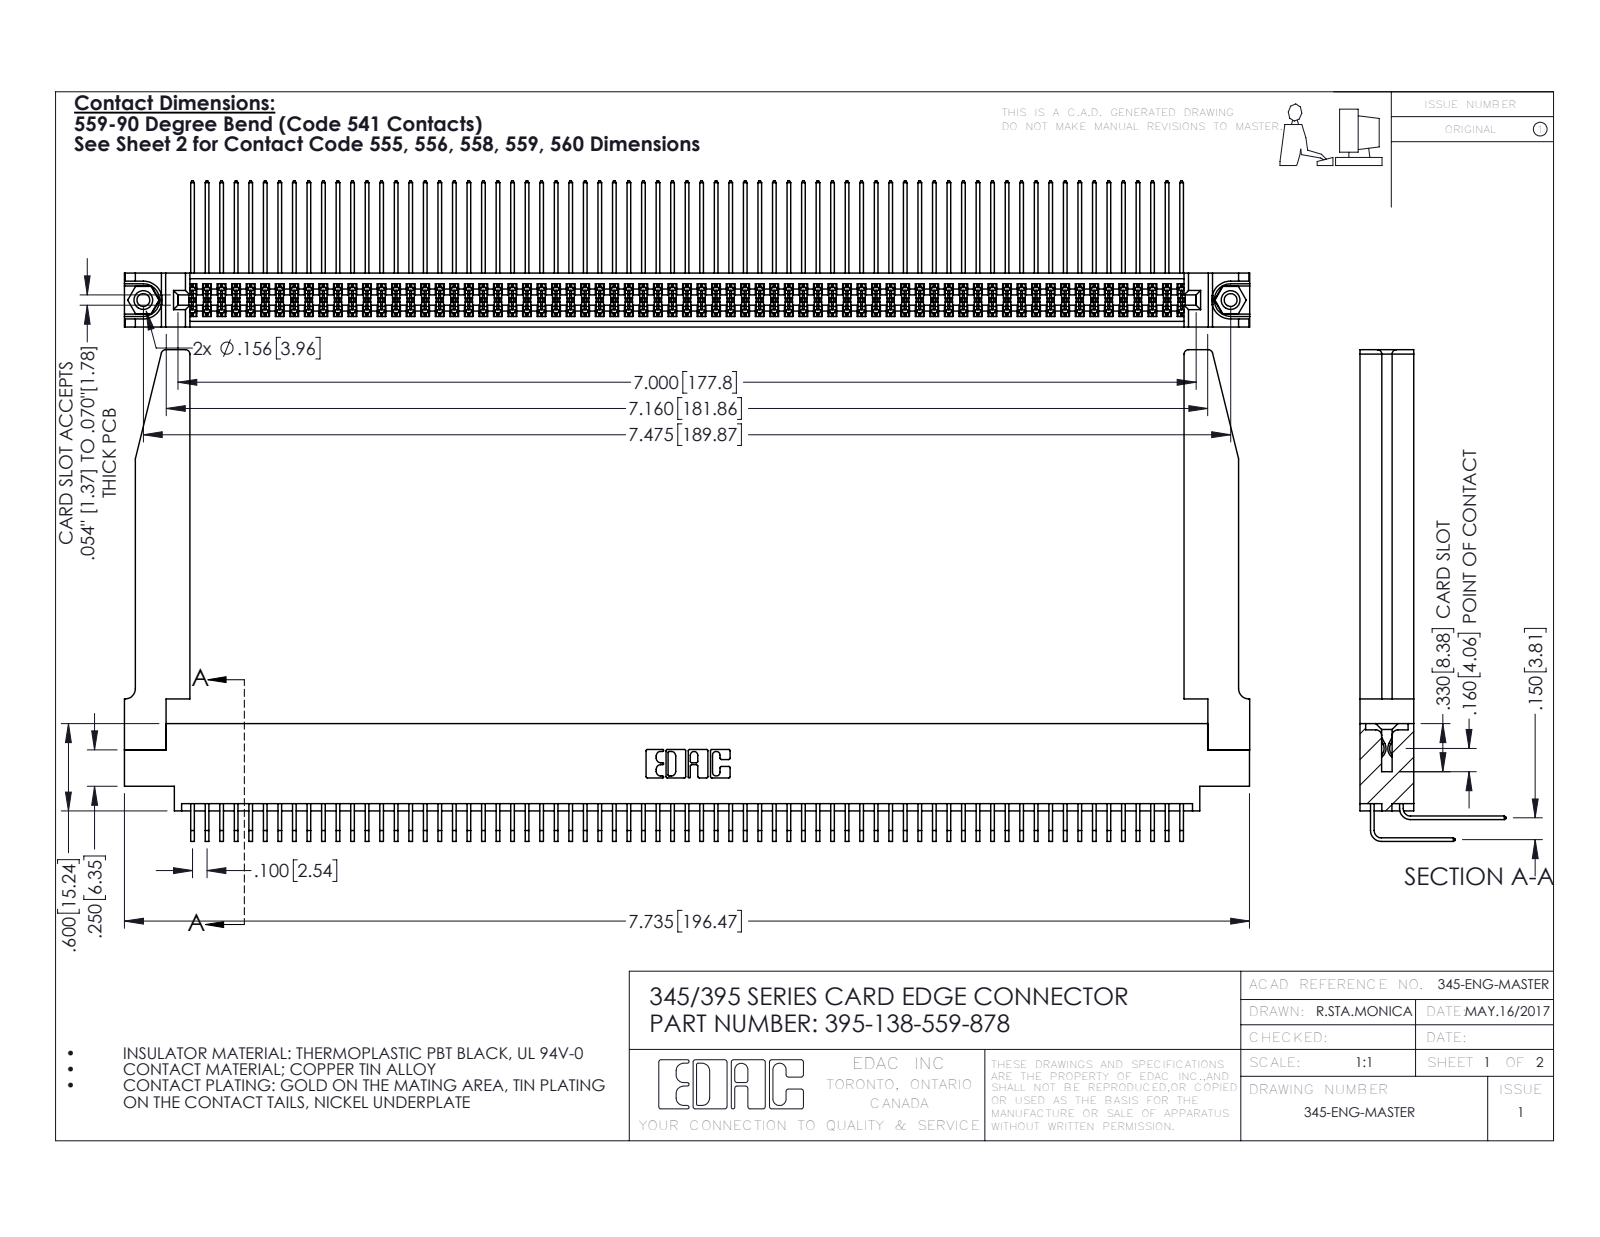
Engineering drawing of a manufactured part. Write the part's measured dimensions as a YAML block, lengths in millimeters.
part_name: "395-138-559-878; 345-292-001_559 Tail - 2; 345-220-078_345-220-078; 345-292-001_558 559 Tail - 1 (+2 more)"
step_written_by: "SolidWorks 2016 (CONFIG_CONTROL_DESIGN)"
units: millimeters
bodies: {solids: 143, faces: 7540, planar: 5056, cylindrical: 2432, other: 52}
overall_size: [196.5, 85.8, 25.5]
volume: 27790
surface_area: 40850
round_holes:
  - {diameter: 2.3, count: 2}
  - {diameter: 3.2, count: 2}
  - {diameter: 4, count: 2}
  - {diameter: 1.6, count: 1}
round_bosses_or_shafts:
  - {diameter: 3.9, count: 2}
partial_cylinders:
  - {radius: 0.2, count: 275}
  - {radius: 0.3, count: 22}
  - {radius: 0.8, count: 8}
  - {radius: 0.2, count: 6}
  - {radius: 0.8, count: 6}
  - {radius: 0.7, count: 3}
  - {radius: 0.4, count: 2}
  - {radius: 0.5, count: 2}
face_to_face_distances: [1.8, 7.6, 9.4, 2.5, 6.9, 0.6, 5.1, 5.7, 4.4, 3.8]
hole_center_spacings: [6.9, 183.9, 189.9]
